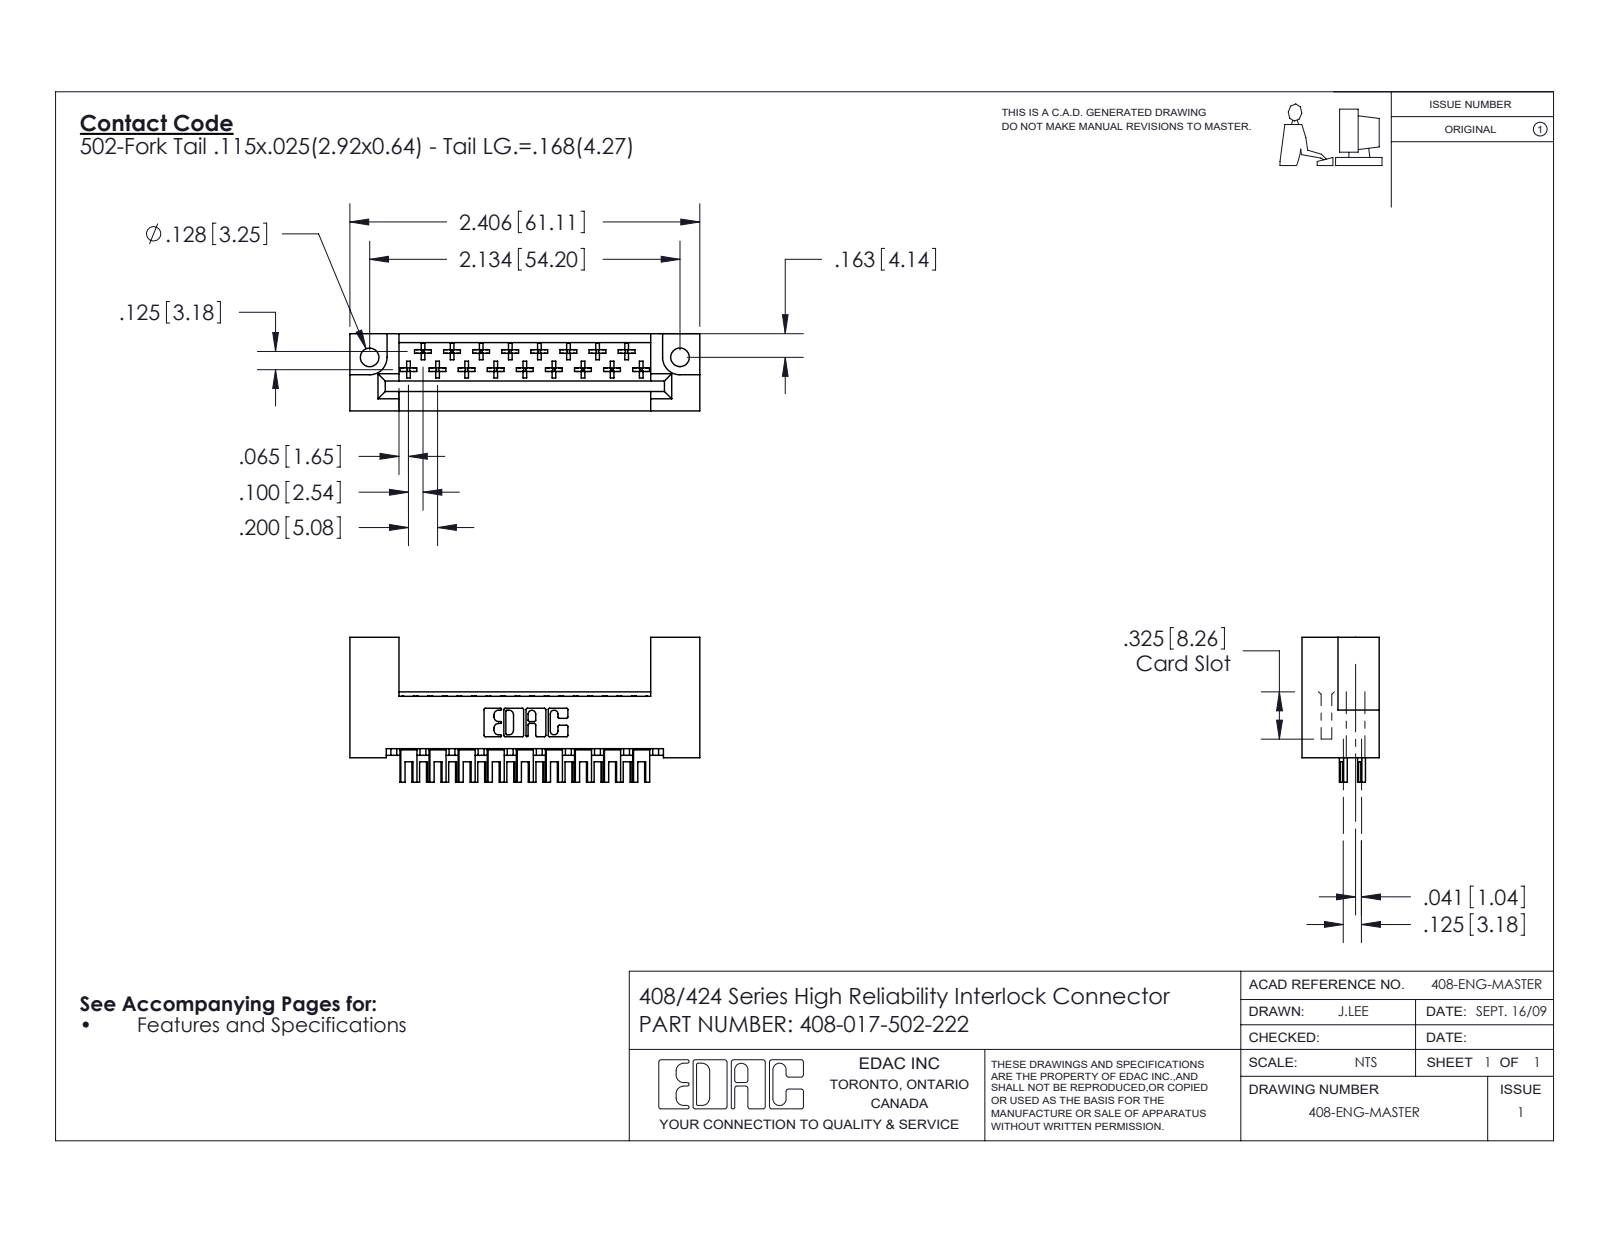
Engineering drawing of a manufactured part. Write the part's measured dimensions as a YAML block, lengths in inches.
part_name: "408-290-001_408-290-102; 408-017-502-222; 408 Part_017 - 2"
step_written_by: "SolidWorks 2016 (CONFIG_CONTROL_DESIGN)"
units: inches
bodies: {solids: 18, faces: 1040, planar: 786, cylindrical: 186, other: 68}
overall_size: [2.406, 0.996, 0.531]
volume: 0.505
surface_area: 13.82
round_holes:
  - {diameter: 0.128, count: 2}
partial_cylinders:
  - {radius: 0.01, count: 102}
  - {radius: 0.01, count: 22}
  - {radius: 0.02, count: 19}
  - {radius: 0.007, count: 6}
  - {radius: 0.031, count: 6}
  - {radius: 0.026, count: 3}
  - {radius: 0.12, count: 2}
face_to_face_distances: [0.531, 0.025, 0.125, 0.1, 0.025, 0.361, 0.326, 0.398, 0.072, 0.205]
hole_center_spacings: [2.134]
